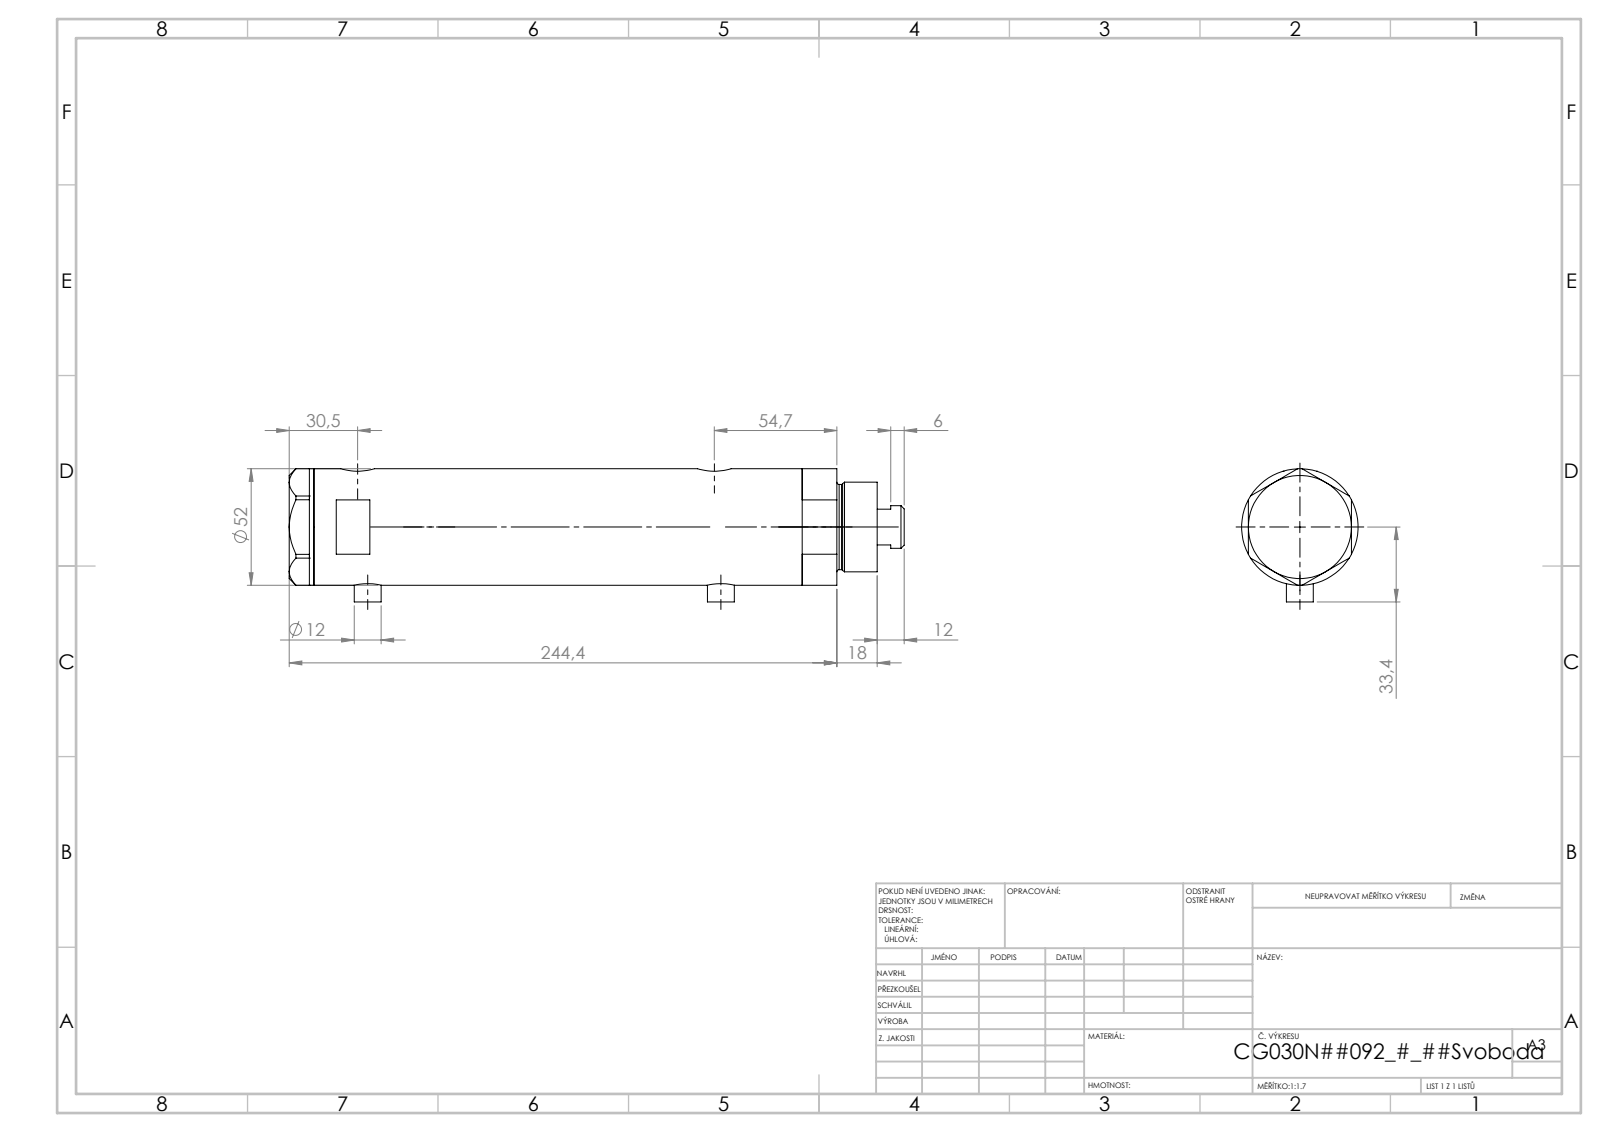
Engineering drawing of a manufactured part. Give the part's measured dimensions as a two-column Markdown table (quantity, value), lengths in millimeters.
| quantity | value |
| --- | --- |
| part name | V270CG_BACK; V270CG_MIDDLE; V270CG_FRONT; V270CG_VC |
| STEP written by | SolidWorks 2019 (CONFIG_CONTROL_DESIGN) |
| units | millimeters |
| bodies | 4 solids, 140 faces (67 planar, 53 cylindrical, 20 other) |
| overall size | 274.4 × 59.4 × 52 |
| volume | 501 068 mm³ |
| surface area | 107 246 mm² |
| round holes (diameter × count) | 5 × 2, 9.73 × 2, 12.5 × 2, 15 × 2, 6.5 × 1, 20 × 1, 21.5 × 1, 30 × 1, 33 × 1, 44 × 1 |
| round bosses / shafts (diameter × count) | 12 × 2, 52 × 1, 40 × 1, 38 × 1, 19 × 1 |
| main face-to-face distances | 181.5, 23.8, 157.7, 11, 34.8, 192.5, 46, 228.9, 217.9, 194.1 |
| hole center spacings | 2.9, 4.5, 154.7, 157.6, 159.2, 162.1 |
